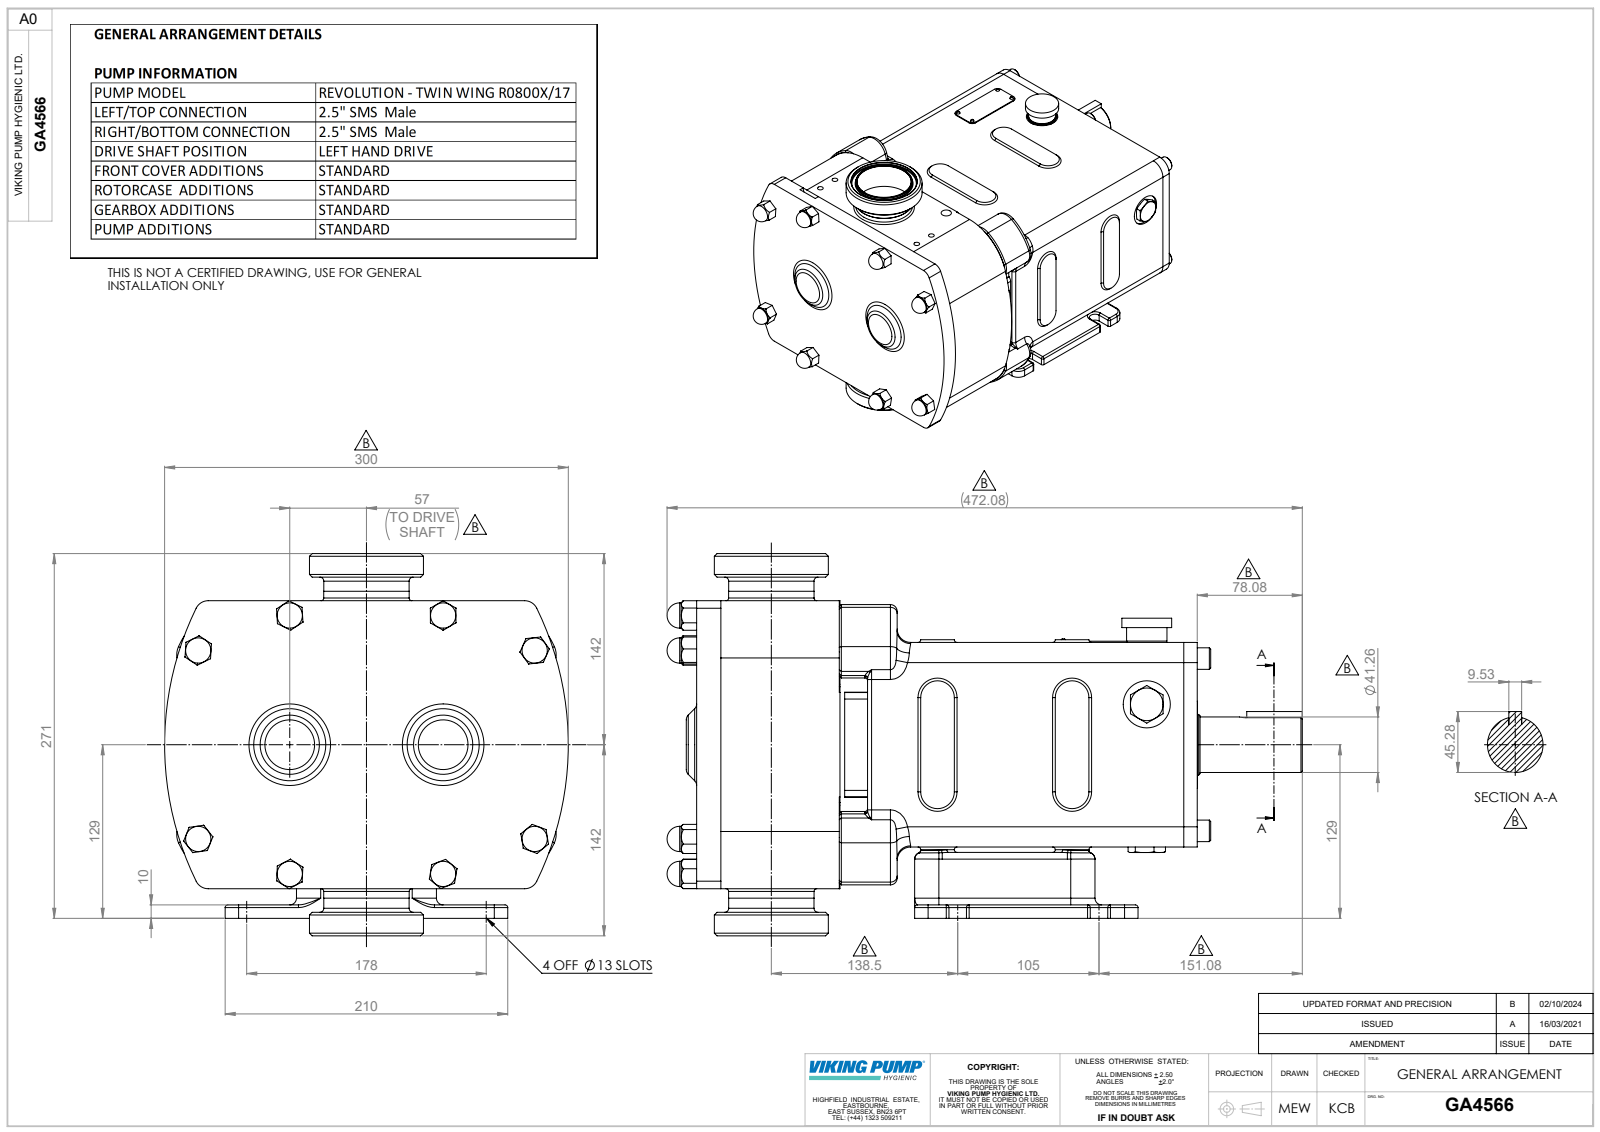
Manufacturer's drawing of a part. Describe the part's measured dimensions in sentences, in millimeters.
The part is named "Copy of R0800 CPP V LHD^GA4566; GA4566; Copy of Z94-5101-44 - 2.5 INCH SMS681^GA4566". Its 3-D file was written by "SolidWorks 2023 (AUTOMOTIVE_DESIGN)". It is 3 solids with 1110 faces: 443 planar, 311 cylindrical and 356 other. Overall it measures 472.07 by 300 by 284 millimeters. Its volume is 17 960 000 cubic millimeters and its surface area 637 253 square millimeters. Round holes: 4 of diameter 6.4, 4 of diameter 35, 2 of diameter 11.5, 1 of diameter 60.3, 1 of diameter 73.5. Round bosses or shafts: 10 of diameter 16, 8 of diameter 18.8, 2 of diameter 29.5, 1 of diameter 84.7, 1 of diameter 63.5, 1 of diameter 63.4, 1 of diameter 63, 1 of diameter 45. Partial cylindrical surfaces (rounded edges, fillets, slot ends): 38 of radius 2, 34 of radius 10, 27 of radius 5, 8 of radius 5.9, 8 of radius 15, 8 of radius 18, 4 of radius 3, 4 of radius 6.5. The main face-to-face distances are 152, 372, 183, 31, 266, 43, 10, 205, 2, 53. The hole center spacings are 23, 46.55, 60, 68.2, 70.21, 76.01, 79.85, 139.63.
